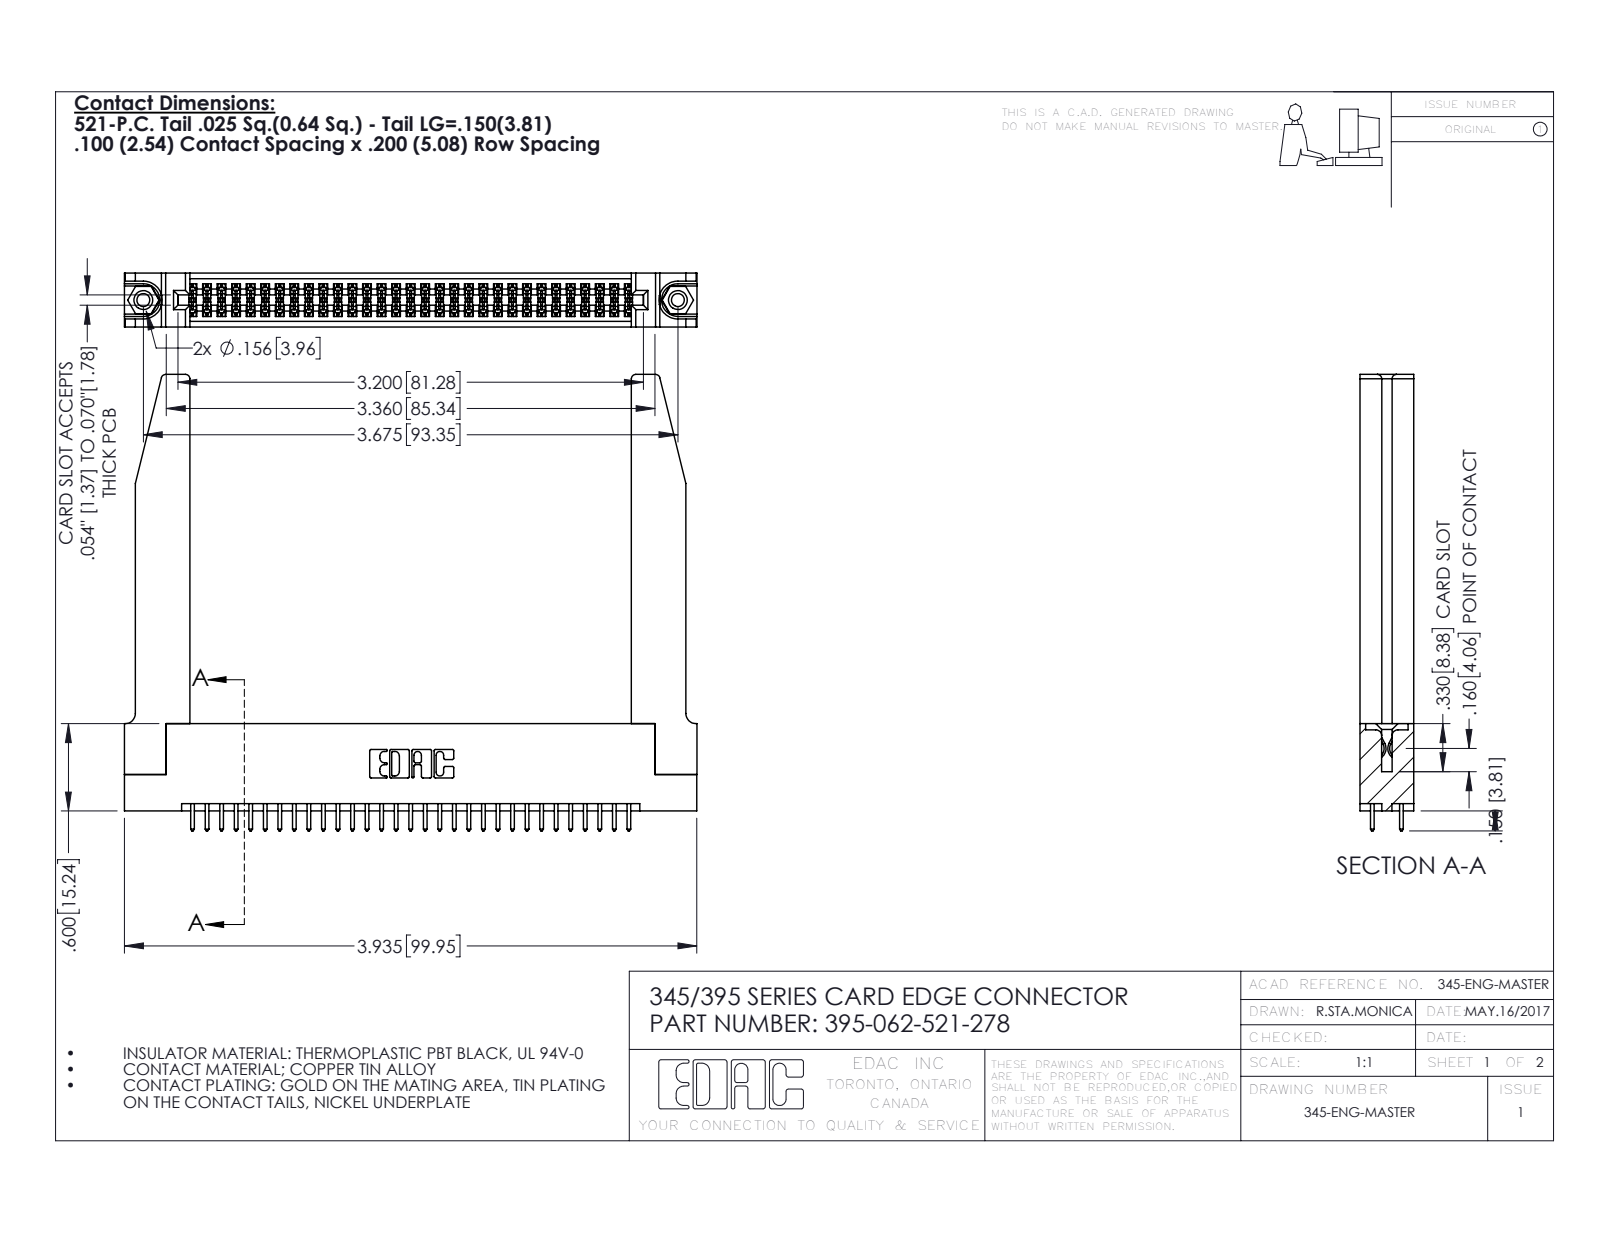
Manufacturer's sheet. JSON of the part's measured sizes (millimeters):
{"part_name": "345-220-078_345-220-078; 345-292-001_345-293-121; 345 Part_Flush Mounting Lugs - 0.156 Dia-TH; 345-250-001_345-250-001-102 (+1 more)", "step_written_by": "SolidWorks 2016 (CONFIG_CONTROL_DESIGN)", "units": "millimeters", "bodies": {"solids": 67, "faces": 3460, "planar": 2268, "cylindrical": 1140, "other": 52}, "overall_size": [100, 79.7, 9.4], "volume_mm3": 17350, "surface_area_mm2": 20630, "round_holes": [[2.3, 2], [3.2, 2], [4, 2], [1.6, 1]], "round_bosses_or_shafts": [[3.9, 2]], "partial_cylinders_radius": [[0.2, 93], [0.3, 62], [0.3, 22], [0.8, 8], [0.2, 6], [0.8, 6], [0.7, 3], [0.4, 2]], "face_to_face_distances": [9.4, 1.8, 7.6, 5.1, 2.5, 6.9, 0.6, 5.7, 3.8, 3.8], "hole_center_spacings": [6.9, 87.4, 93.3]}
